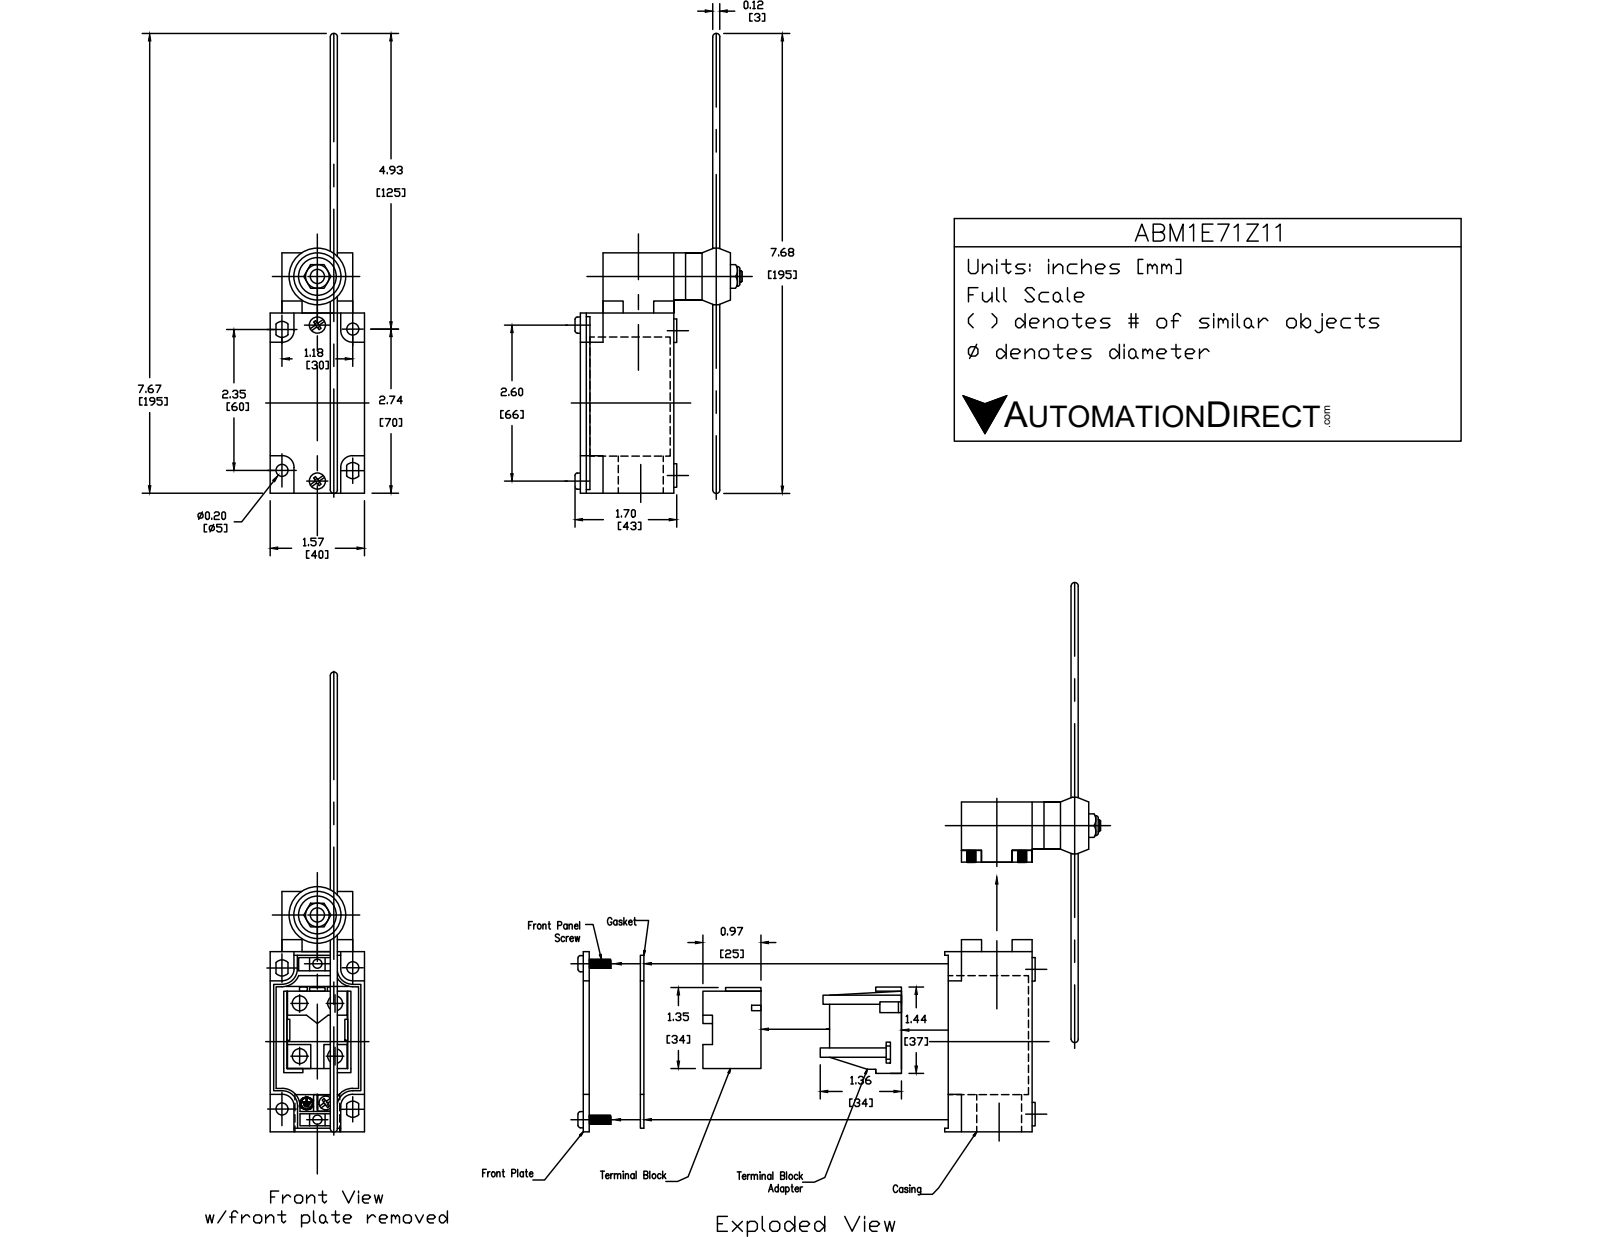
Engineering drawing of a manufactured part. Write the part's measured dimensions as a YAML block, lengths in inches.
part_name: "ABM1E71Z11"
step_written_by: "SolidWorks 2017 (AUTOMOTIVE_DESIGN)"
units: inches
bodies: {solids: 5, faces: 238, planar: 116, cylindrical: 89, other: 33}
overall_size: [7.672, 2.335, 1.575]
volume: 8.642
surface_area: 45.88
round_holes:
  - {diameter: 0.205, count: 2}
  - {diameter: 0.118, count: 1}
  - {diameter: 0.236, count: 1}
  - {diameter: 0.551, count: 1}
  - {diameter: 0.669, count: 1}
  - {diameter: 0.748, count: 1}
round_bosses_or_shafts:
  - {diameter: 0.394, count: 5}
  - {diameter: 0.276, count: 2}
  - {diameter: 0.945, count: 1}
  - {diameter: 0.787, count: 1}
  - {diameter: 0.236, count: 1}
partial_cylinders:
  - {radius: 0.059, count: 16}
  - {radius: 0.039, count: 4}
  - {radius: 0.197, count: 4}
  - {radius: 0.128, count: 2}
  - {radius: 0.453, count: 1}
  - {radius: 0.472, count: 1}
face_to_face_distances: [1.575, 1.555, 0.197, 1.181, 1.378, 3.012, 0.984, 0.374, 0.177, 4.016]
hole_center_spacings: [1.394, 0.551, 1.048, 2.641, 3.282]
